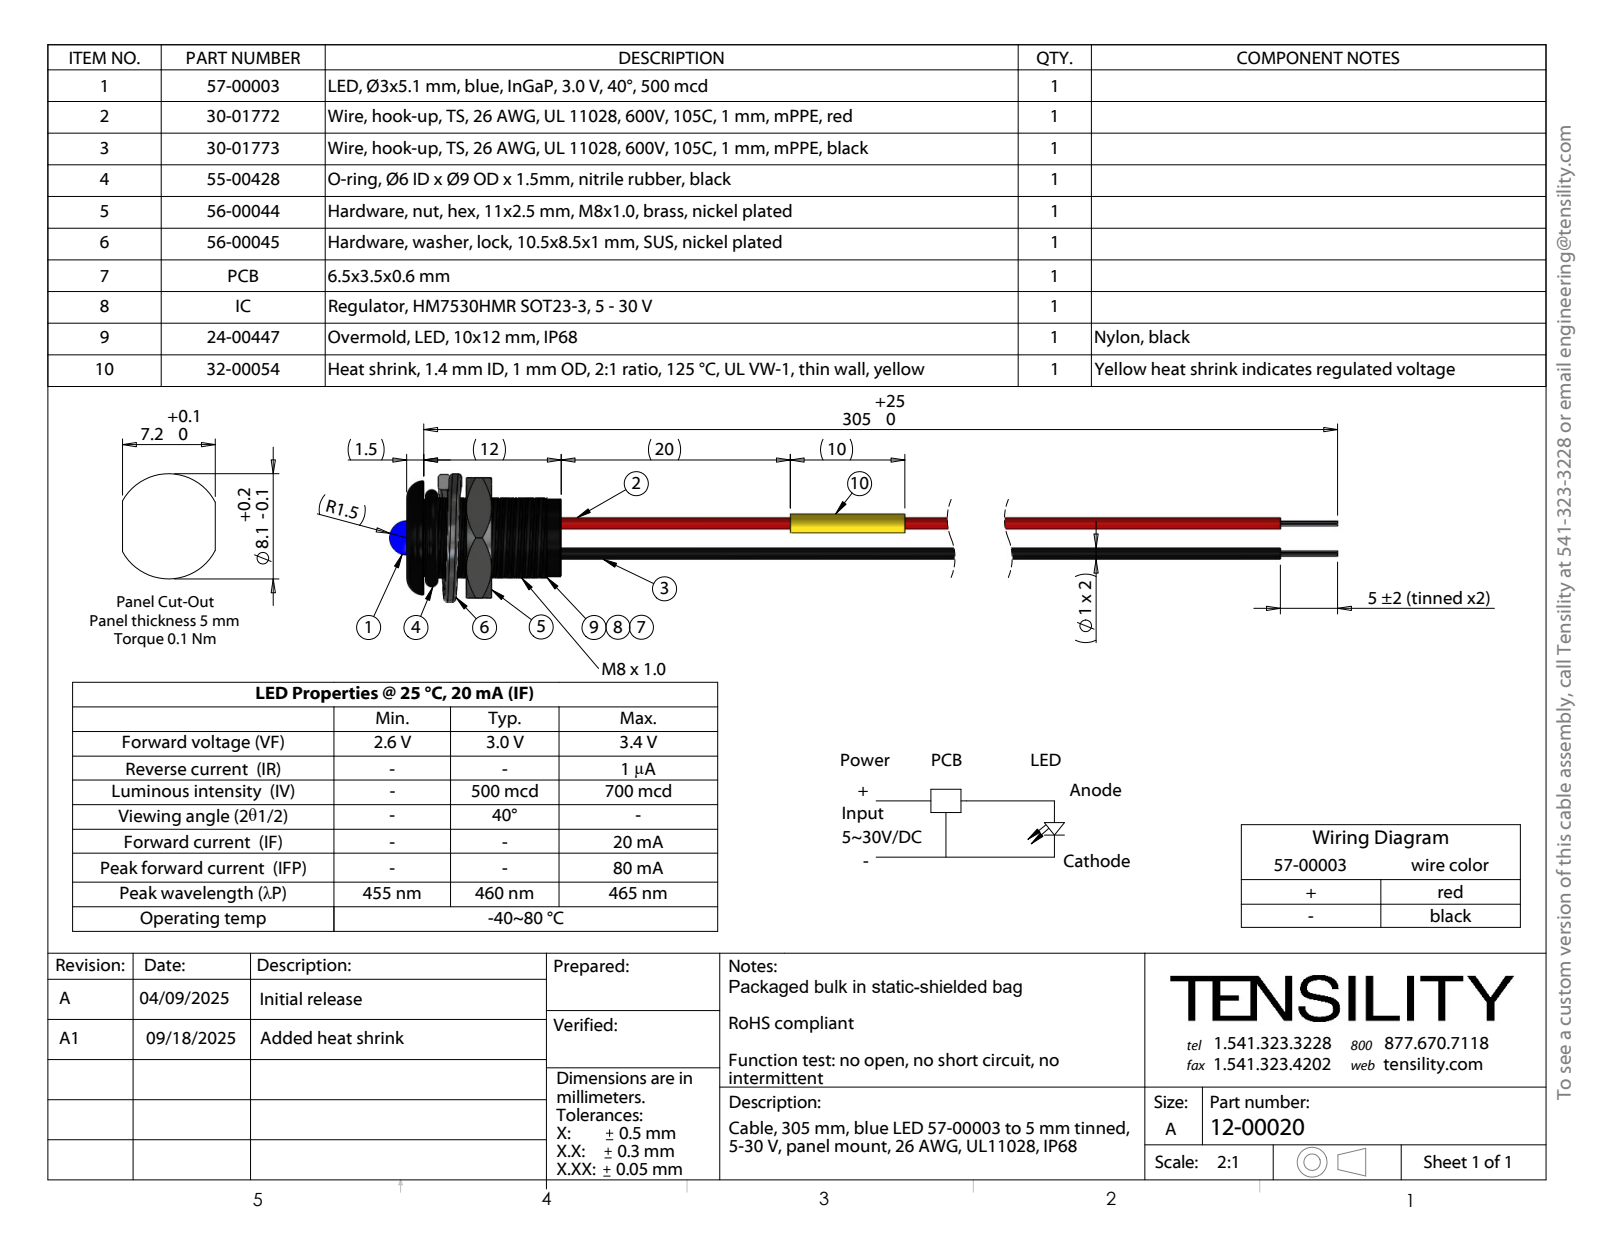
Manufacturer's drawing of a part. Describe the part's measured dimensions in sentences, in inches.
The part is named "56-00045_Split washer; 12-00020; 55-00428; 30-01772_stripped and tinned (+5 more)". Its 3-D file was written by "SolidWorks 2021 (CONFIG_CONTROL_DESIGN)". It is 57 solids with 555 faces: 186 planar, 246 cylindrical and 123 other. Overall it measures 6.693 by 0.477 by 0.441 inches. Its volume is 0.061 cubic inches and its surface area 9.157 square inches. Round holes: 2 of diameter 0.039. Round bosses or shafts: 2 of diameter 0.039, 2 of diameter 0.02, 1 of diameter 0.268, 1 of diameter 0.118. Partial cylindrical surfaces (rounded edges, fillets, slot ends): 1 of radius 0.137, 1 of radius 0.157. The main face-to-face distances are 0.059, 0.531, 0.472, 0.413, 0.205, 0.146, 0.326, 0.292, 0.233, 0.087. The hole center spacings are 0.014, 0.015, 0.013, 0.098, 0.099, 0.096, 0.096, 0.101.
